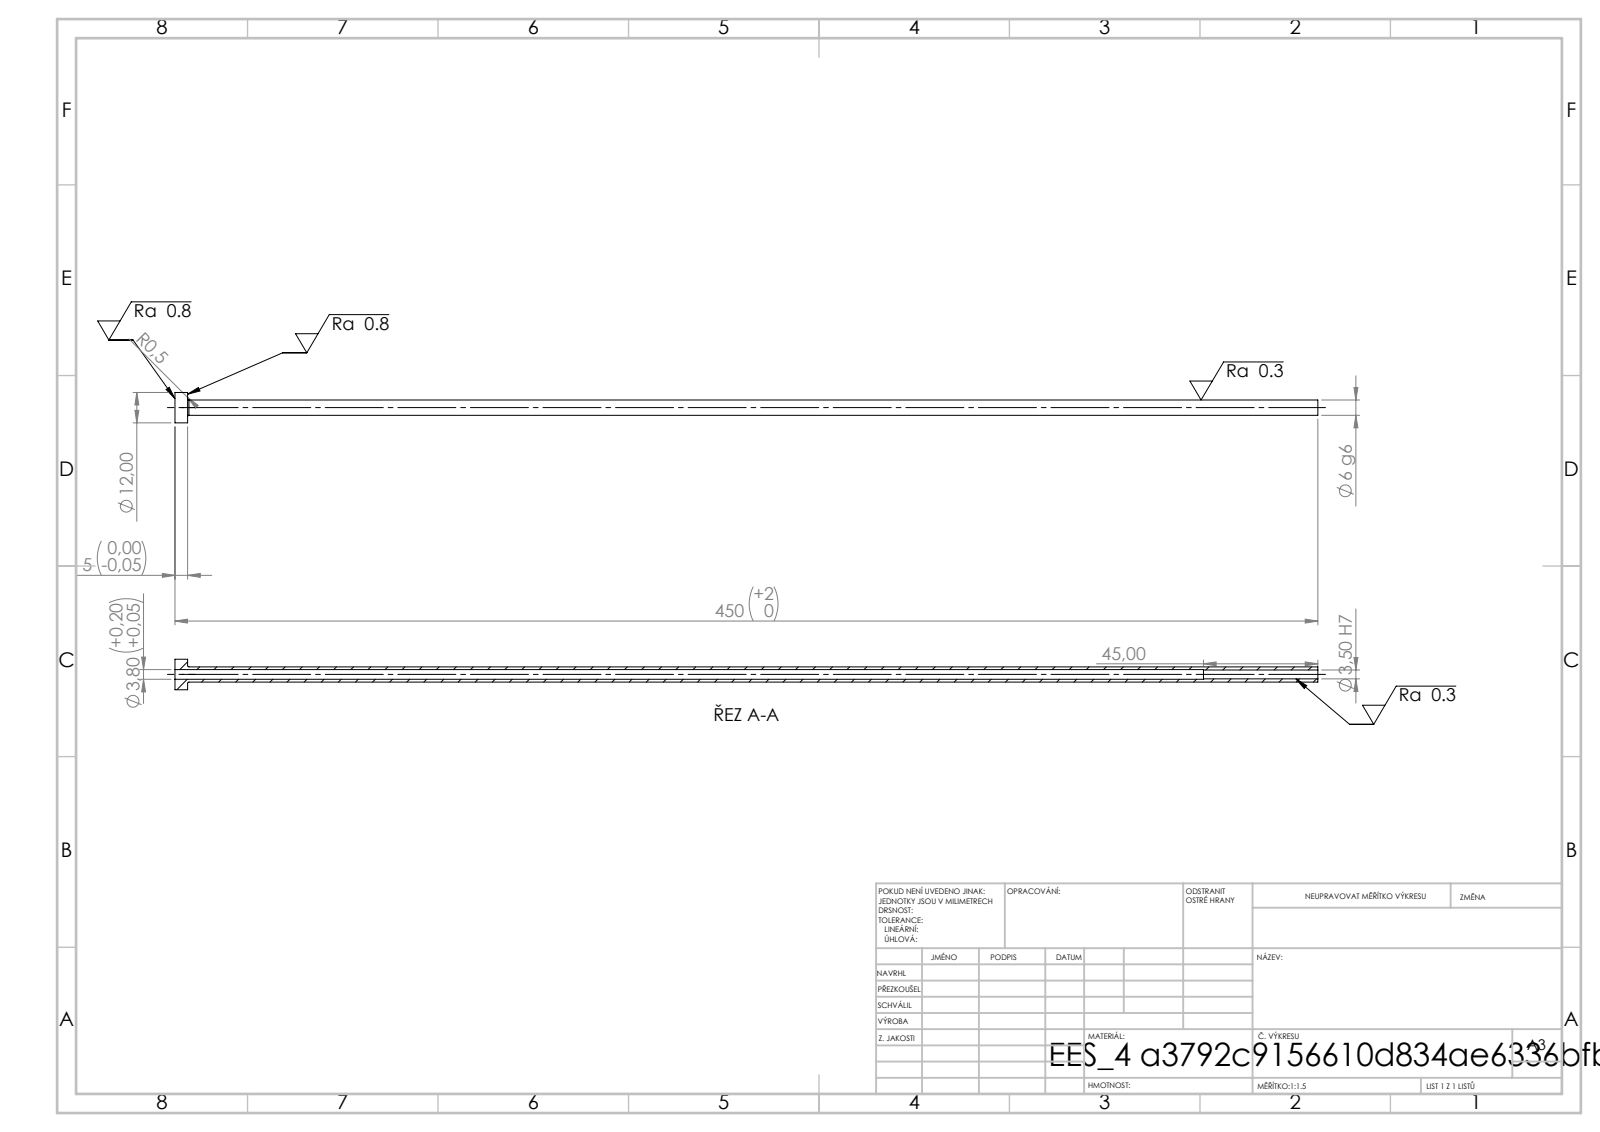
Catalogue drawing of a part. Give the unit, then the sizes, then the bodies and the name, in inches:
Units: inches
Overall size (bounding box): 17.717 × 0.472 × 0.472
Round holes (diameter × count): ⌀0.138 ×1, ⌀0.15 ×1
Round bosses / shafts (diameter × count): ⌀0.472 ×1, ⌀0.236 ×1
Main face-to-face distances: 0.197, 17.717, 17.52, 15.945, 15.748, 1.772
Volume: 0.496 in³ · Surface area: 21.87 in²
Bodies: 1 solid, 14 faces (4 planar, 8 cylindrical, 2 other)
STEP written by: SolidWorks 2019 (CONFIG_CONTROL_DESIGN)
